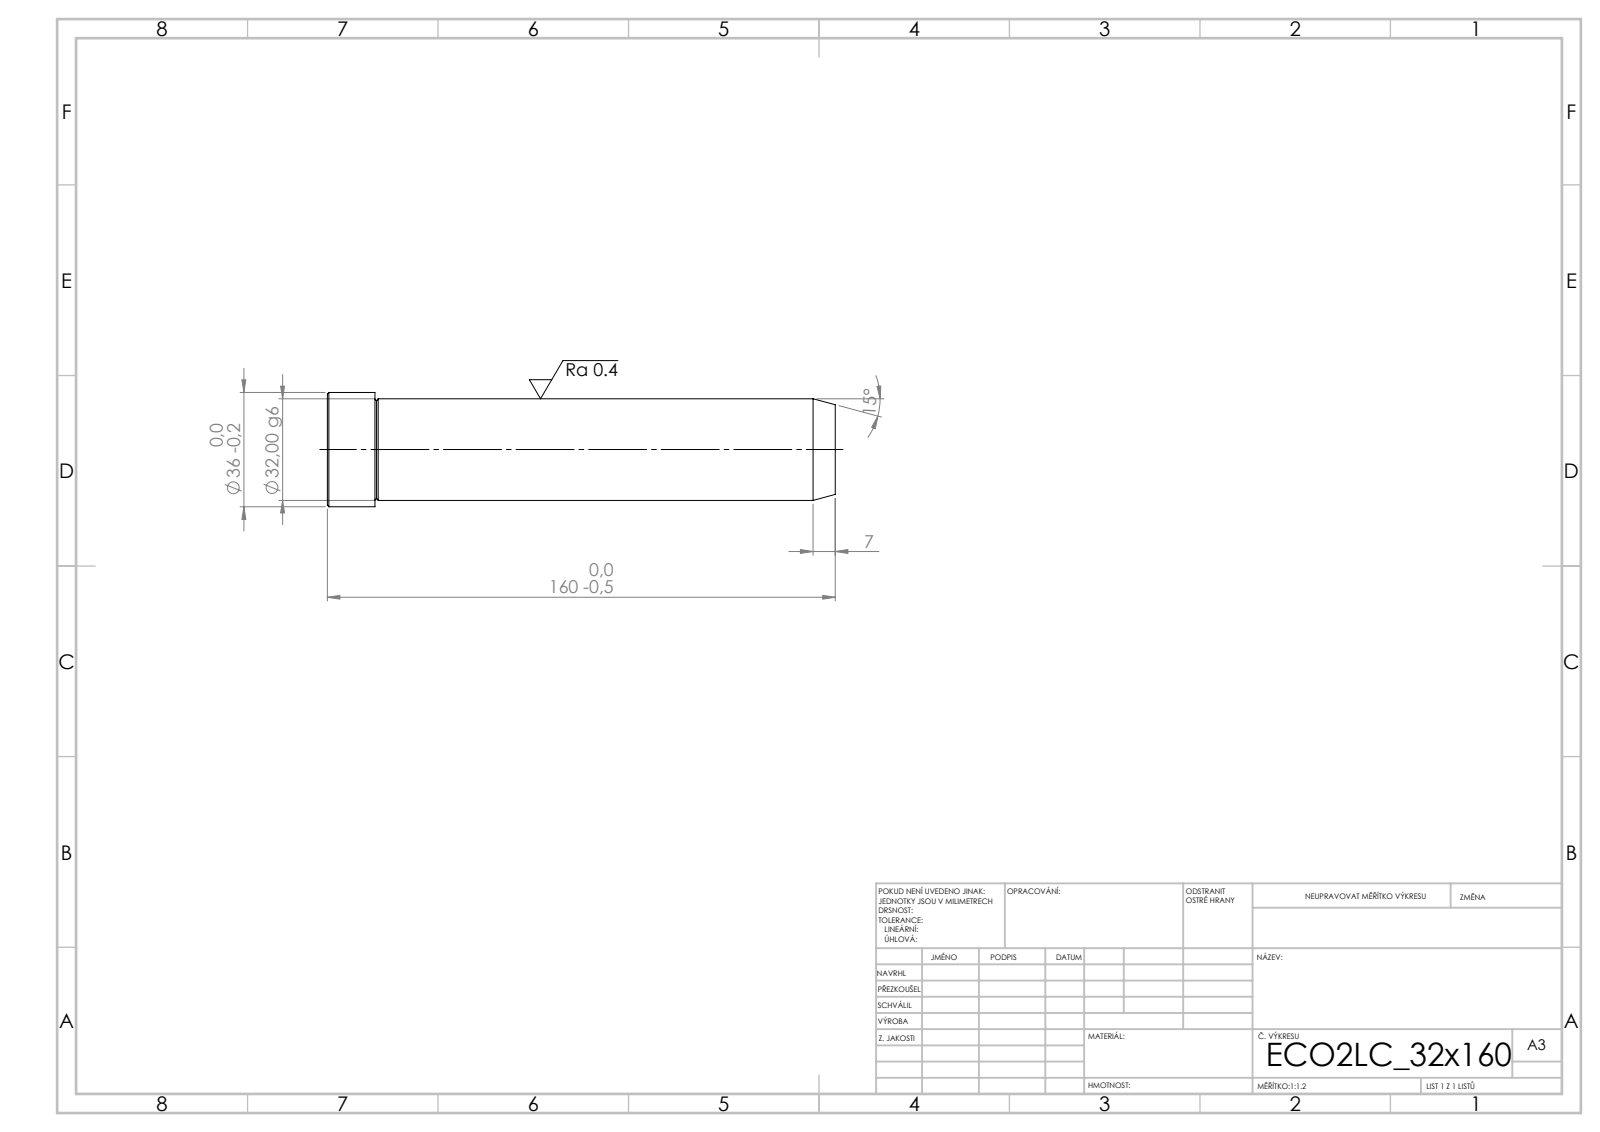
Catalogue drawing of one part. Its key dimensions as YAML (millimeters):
step_written_by: "SolidWorks 2019 (CONFIG_CONTROL_DESIGN)"
units: millimeters
bodies: {solids: 1, faces: 15, planar: 3, cylindrical: 4, other: 8}
overall_size: [160, 36, 36]
volume: 131197
surface_area: 18135
round_bosses_or_shafts:
  - {diameter: 36, count: 1}
  - {diameter: 32, count: 1}
face_to_face_distances: [160, 145, 15]
